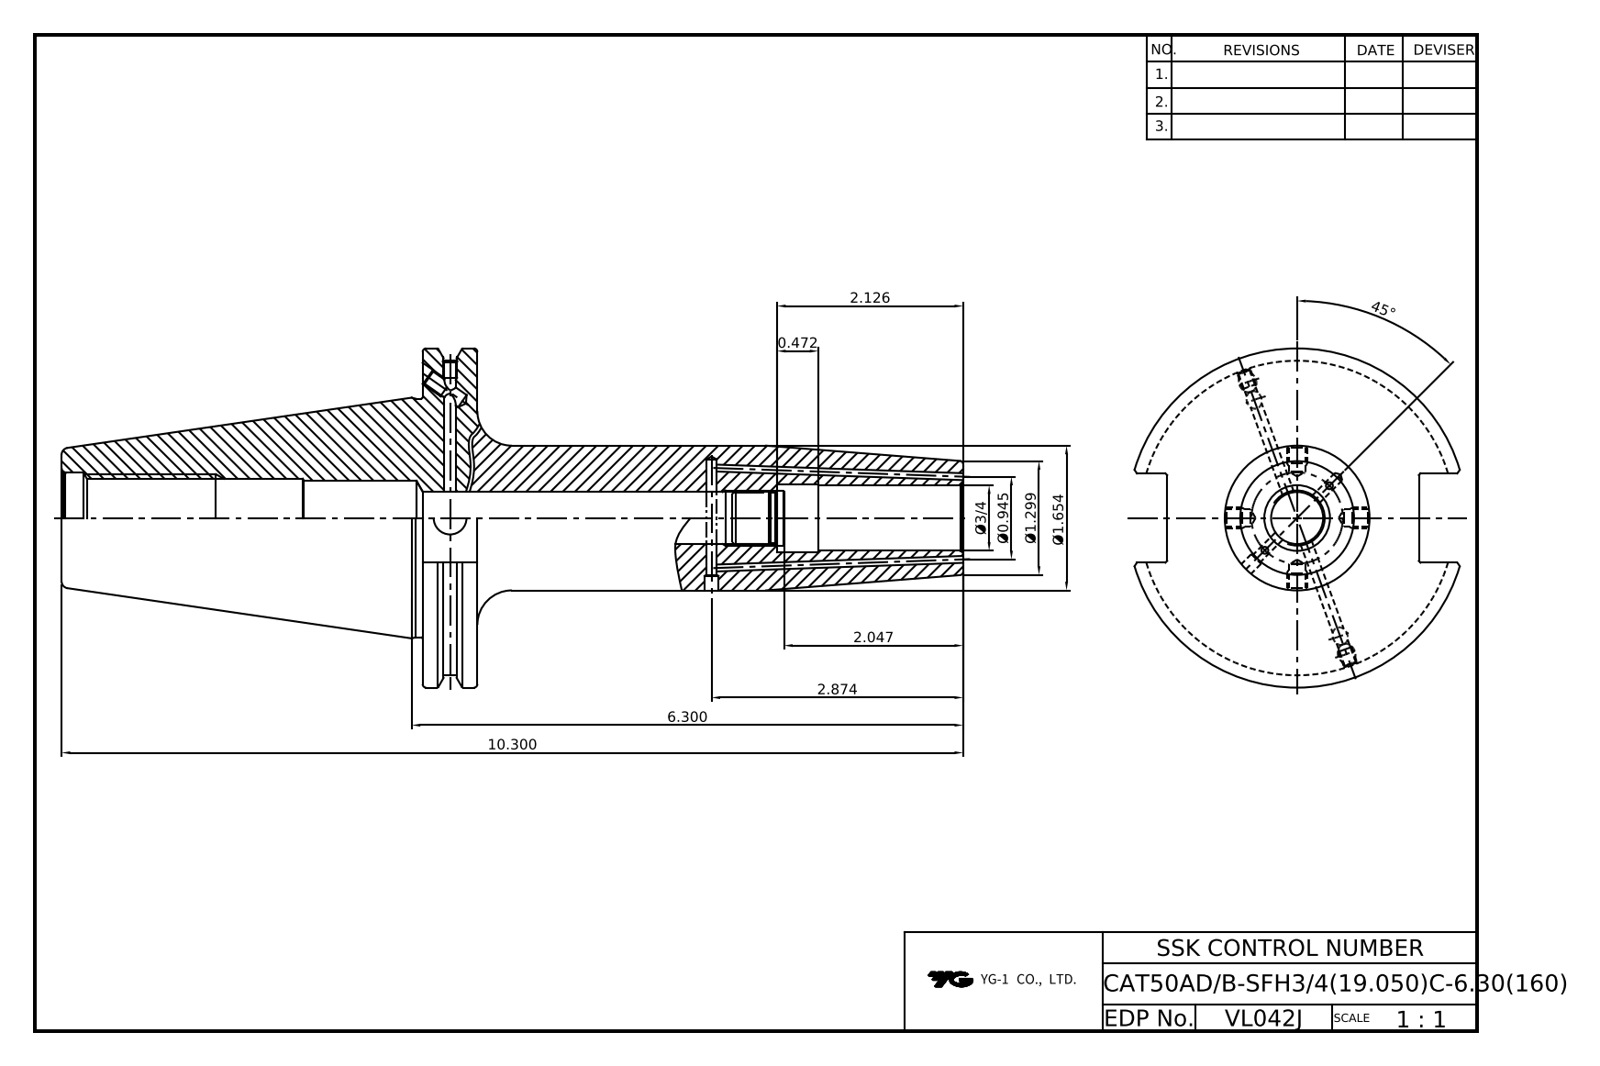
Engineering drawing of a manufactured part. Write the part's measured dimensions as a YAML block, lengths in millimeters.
part_name: "LO-CAT50ADB-SFH19.05C-160"
step_written_by: "Autodesk Inventor 2025 (AUTOMOTIVE_DESIGN)"
units: millimeters
bodies: {solids: 1, faces: 88, planar: 37, cylindrical: 28, other: 23}
overall_size: [261.6, 98.42, 94.69]
volume: 462742
surface_area: 70594
round_holes:
  - {diameter: 2.5, count: 2}
  - {diameter: 3.24, count: 2}
  - {diameter: 4.13, count: 2}
  - {diameter: 4.2, count: 2}
  - {diameter: 5, count: 2}
  - {diameter: 9.53, count: 1}
  - {diameter: 14.92, count: 1}
  - {diameter: 19.05, count: 1}
  - {diameter: 20.25, count: 1}
  - {diameter: 21.97, count: 1}
  - {diameter: 26.2, count: 1}
round_bosses_or_shafts:
  - {diameter: 98.42, count: 1}
  - {diameter: 91.29, count: 1}
  - {diameter: 69.25, count: 1}
  - {diameter: 42, count: 1}
face_to_face_distances: [15.88, 104.77, 120.65, 261.6, 156.83, 140.95, 73.03, 25.9, 110.82, 6.05]
